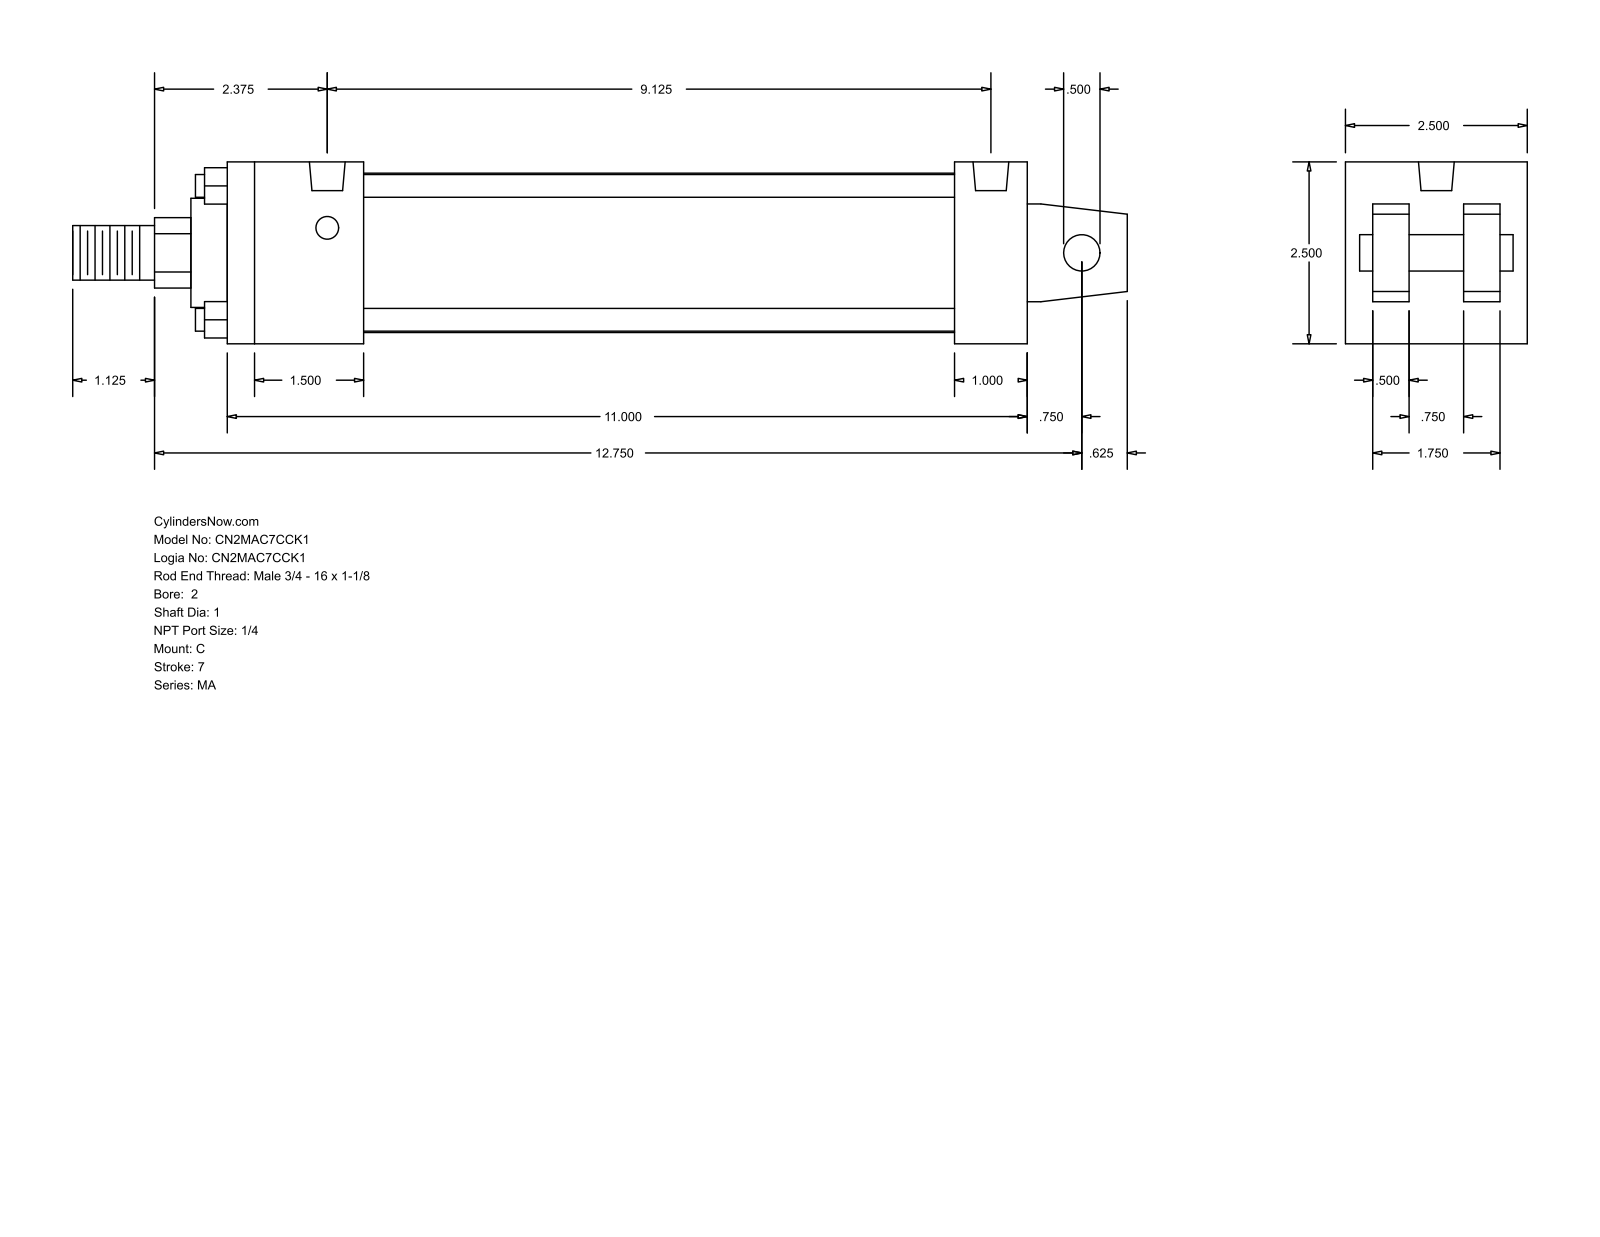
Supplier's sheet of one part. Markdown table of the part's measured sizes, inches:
| quantity | value |
| --- | --- |
| part name | MA_C__0200_1 |
| STEP written by | GSSL Pune (CONFIG_CONTROL_DESIGN) |
| units | inches |
| bodies | 0 solids, 103 faces (76 planar, 27 cylindrical, 0 other) |
| overall size | 14.5 × 2.5 × 2.5 |
| round holes (diameter × count) | 0.313 × 4, 0.492 × 2 |
| round bosses / shafts (diameter × count) | 0.313 × 4, 2.19 × 1, 1.5 × 1, 1 × 1, 0.75 × 1, 0.5 × 1 |
| partial cylindrical surfaces (radius × count) | 0.484 × 1 |
| main face-to-face distances | 2.5, 0.5, 11, 0.875, 1.625, 0.375, 2.125, 1.25, 1.875, 1 |
| hole center spacings | 9.125 |
